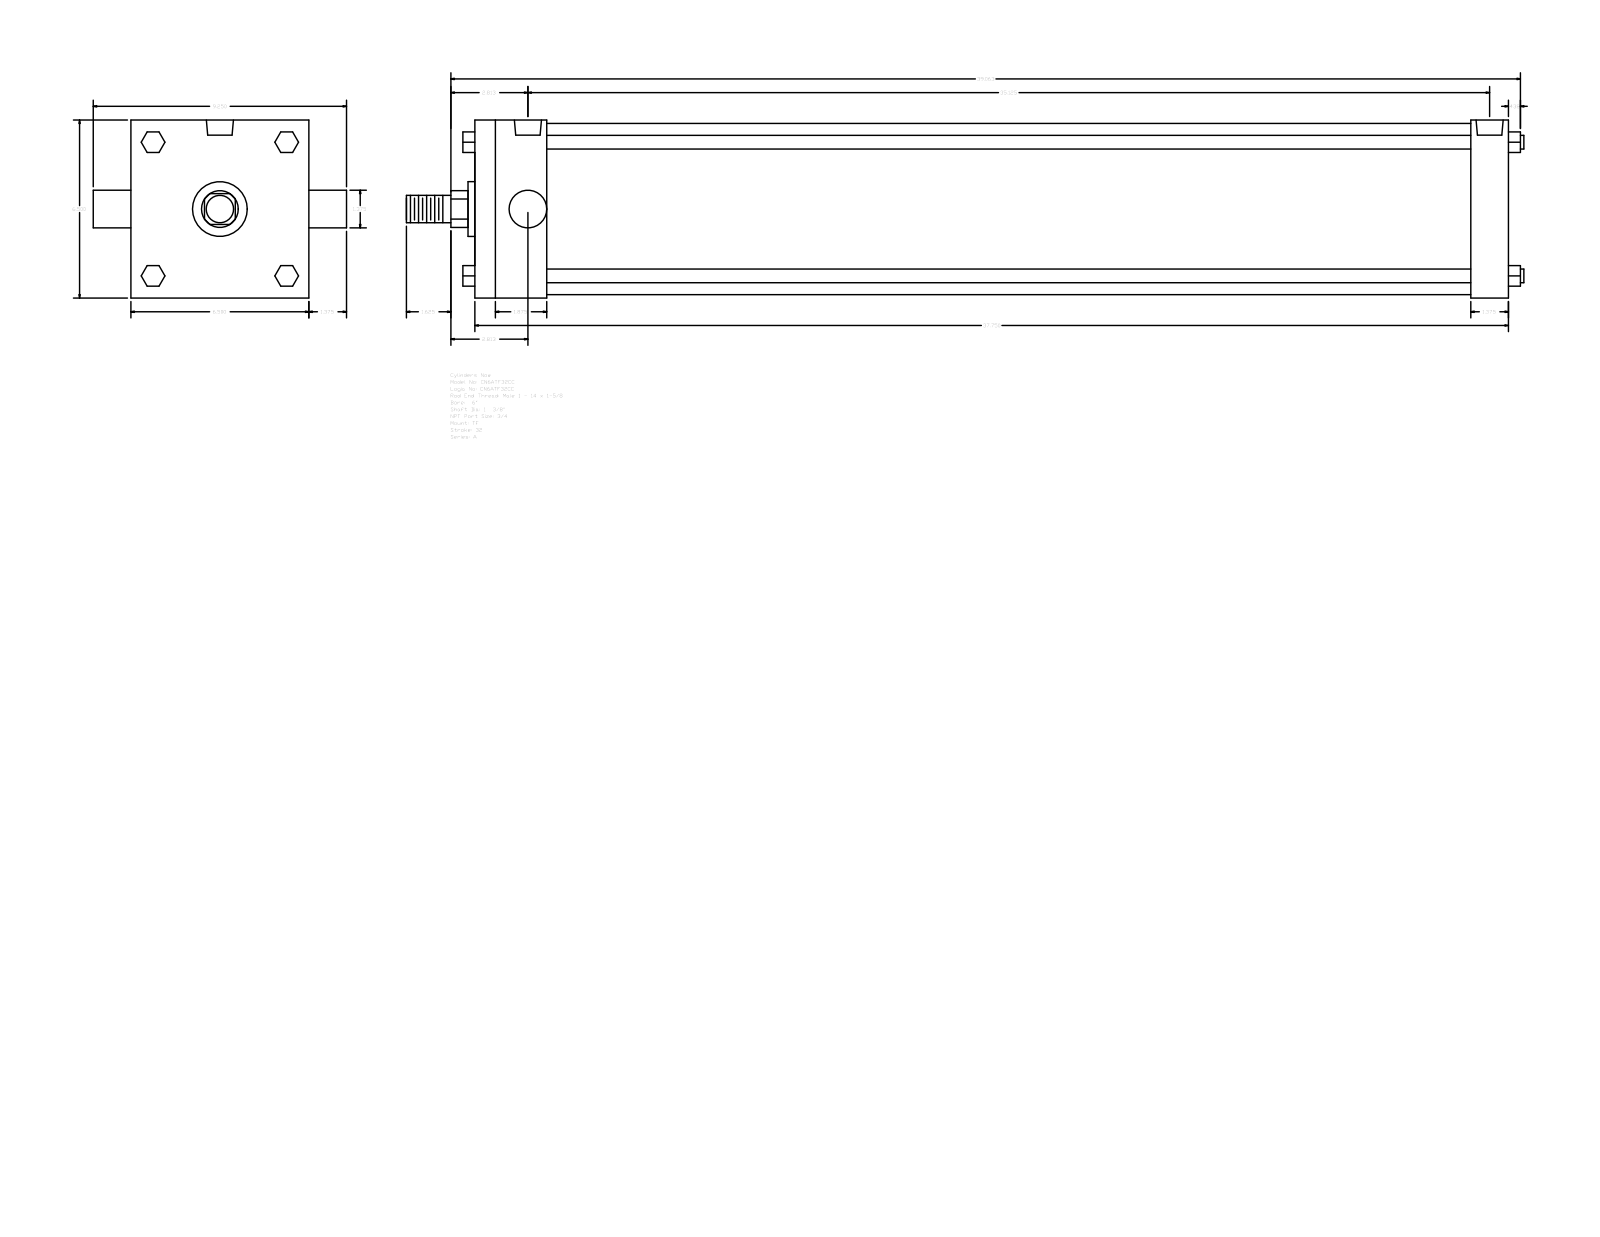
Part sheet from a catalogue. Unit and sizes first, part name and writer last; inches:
Units: inches
Overall size (bounding box): 40.813 × 9.25 × 6.5
Round holes (diameter × count): ⌀0.594 ×3, ⌀0.989 ×2
Round bosses / shafts (diameter × count): ⌀0.5 ×4, ⌀1.375 ×2, ⌀6.25 ×1, ⌀2 ×1, ⌀1 ×1
Partial cylindrical surfaces — rounded edges, fillets, slot ends (radius × count): R0.672 ×1
Main face-to-face distances: 6.5, 37.75, 2.625, 35.125, 36.375, 33.75, 1.375, 0.75, 2.44, 4.226
Hole centre spacings: 0.219, 34.906, 34.687, 35.125
Bodies: 0 solids, 120 faces (92 planar, 28 cylindrical, 0 other)
Part name (STEP PRODUCT): A_TF__0600_1.375
STEP written by: GSSL Pune (CONFIG_CONTROL_DESIGN)
